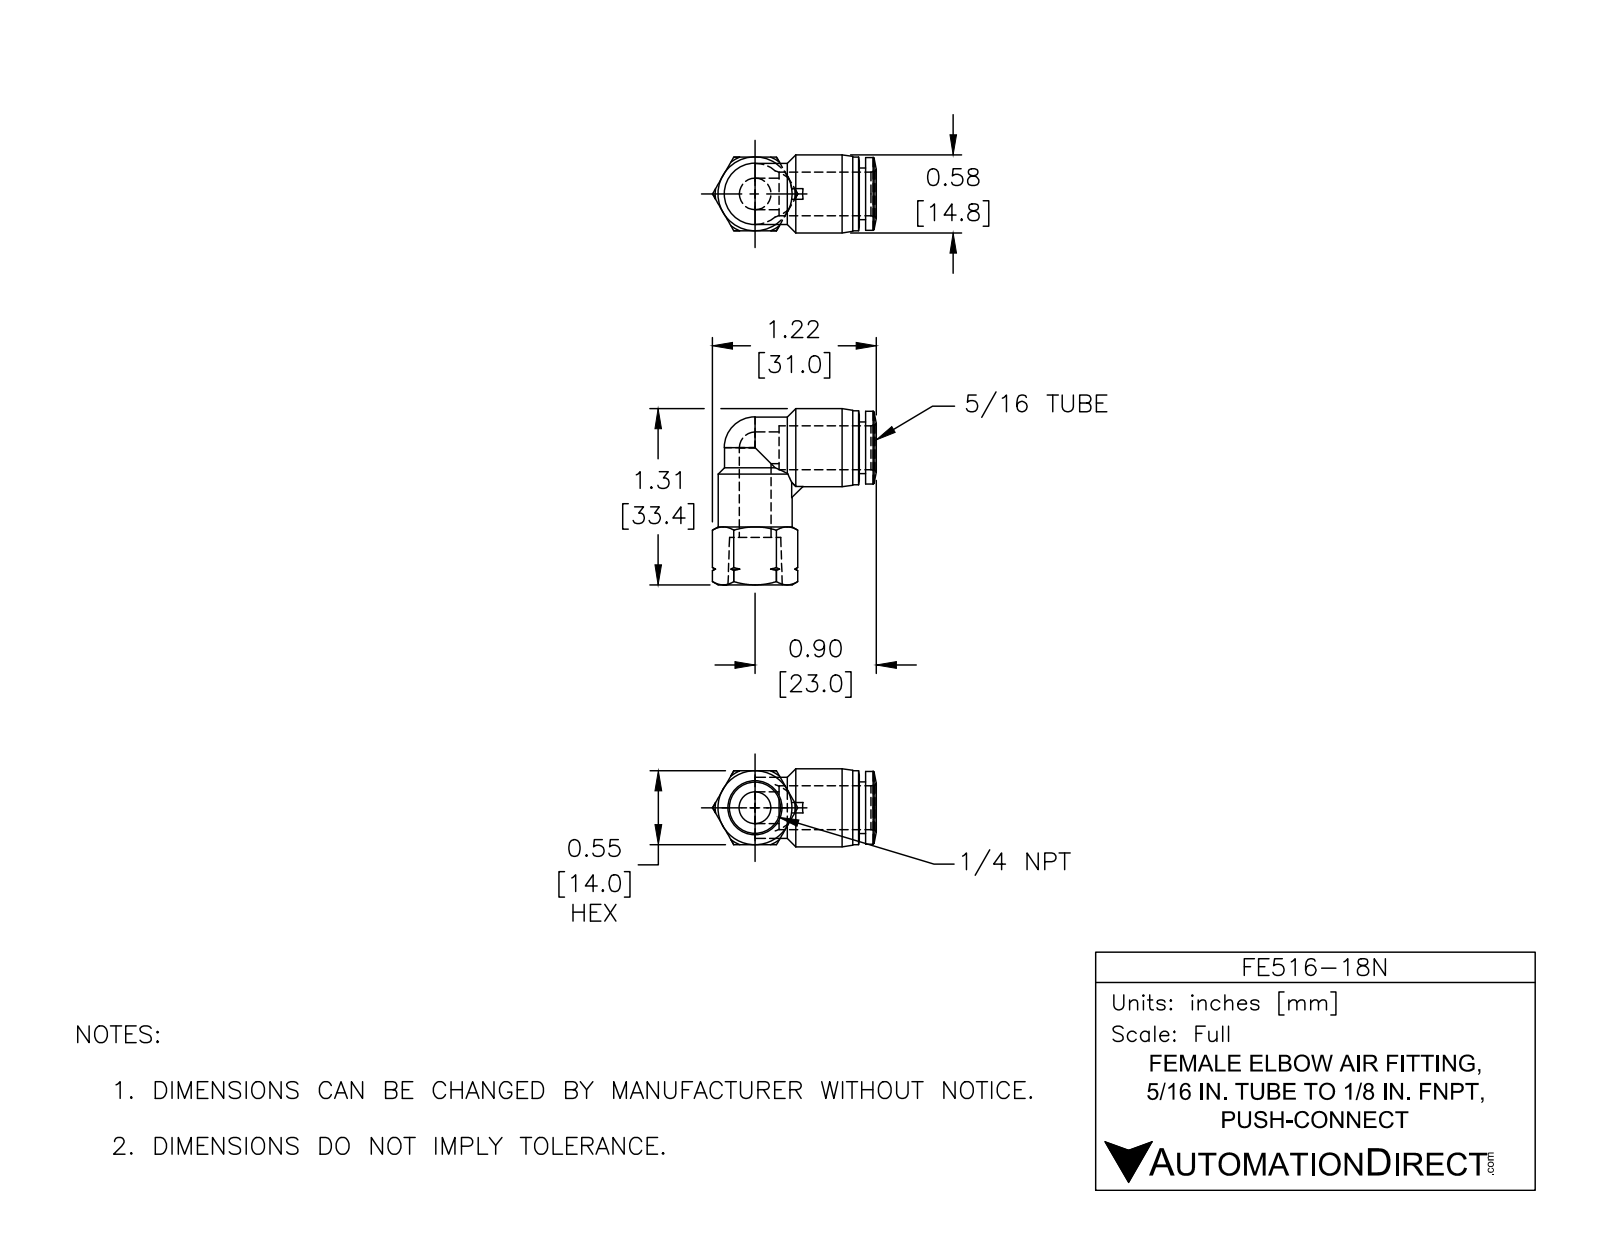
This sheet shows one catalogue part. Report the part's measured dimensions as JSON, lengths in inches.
{"part_name": "FE516-18N", "step_written_by": "SolidWorks 2015 (CONFIG_CONTROL_DESIGN)", "units": "inches", "bodies": {"solids": 1, "faces": 86, "planar": 15, "cylindrical": 21, "other": 50}, "overall_size": [1.315, 1.222, 0.583], "volume_in3": 0.296, "surface_area_in2": 5.692, "round_holes": [[0.236, 2], [0.327, 1]], "round_bosses_or_shafts": [[0.551, 2], [0.583, 1], [0.543, 1], [0.457, 1], [0.386, 1]], "partial_cylinders_radius": [[0.228, 1]], "face_to_face_distances": [0.551, 0.047, 0.354, 0.598, 0.646, 0.236, 0.315, 0.549, 0.049, 0.096]}
